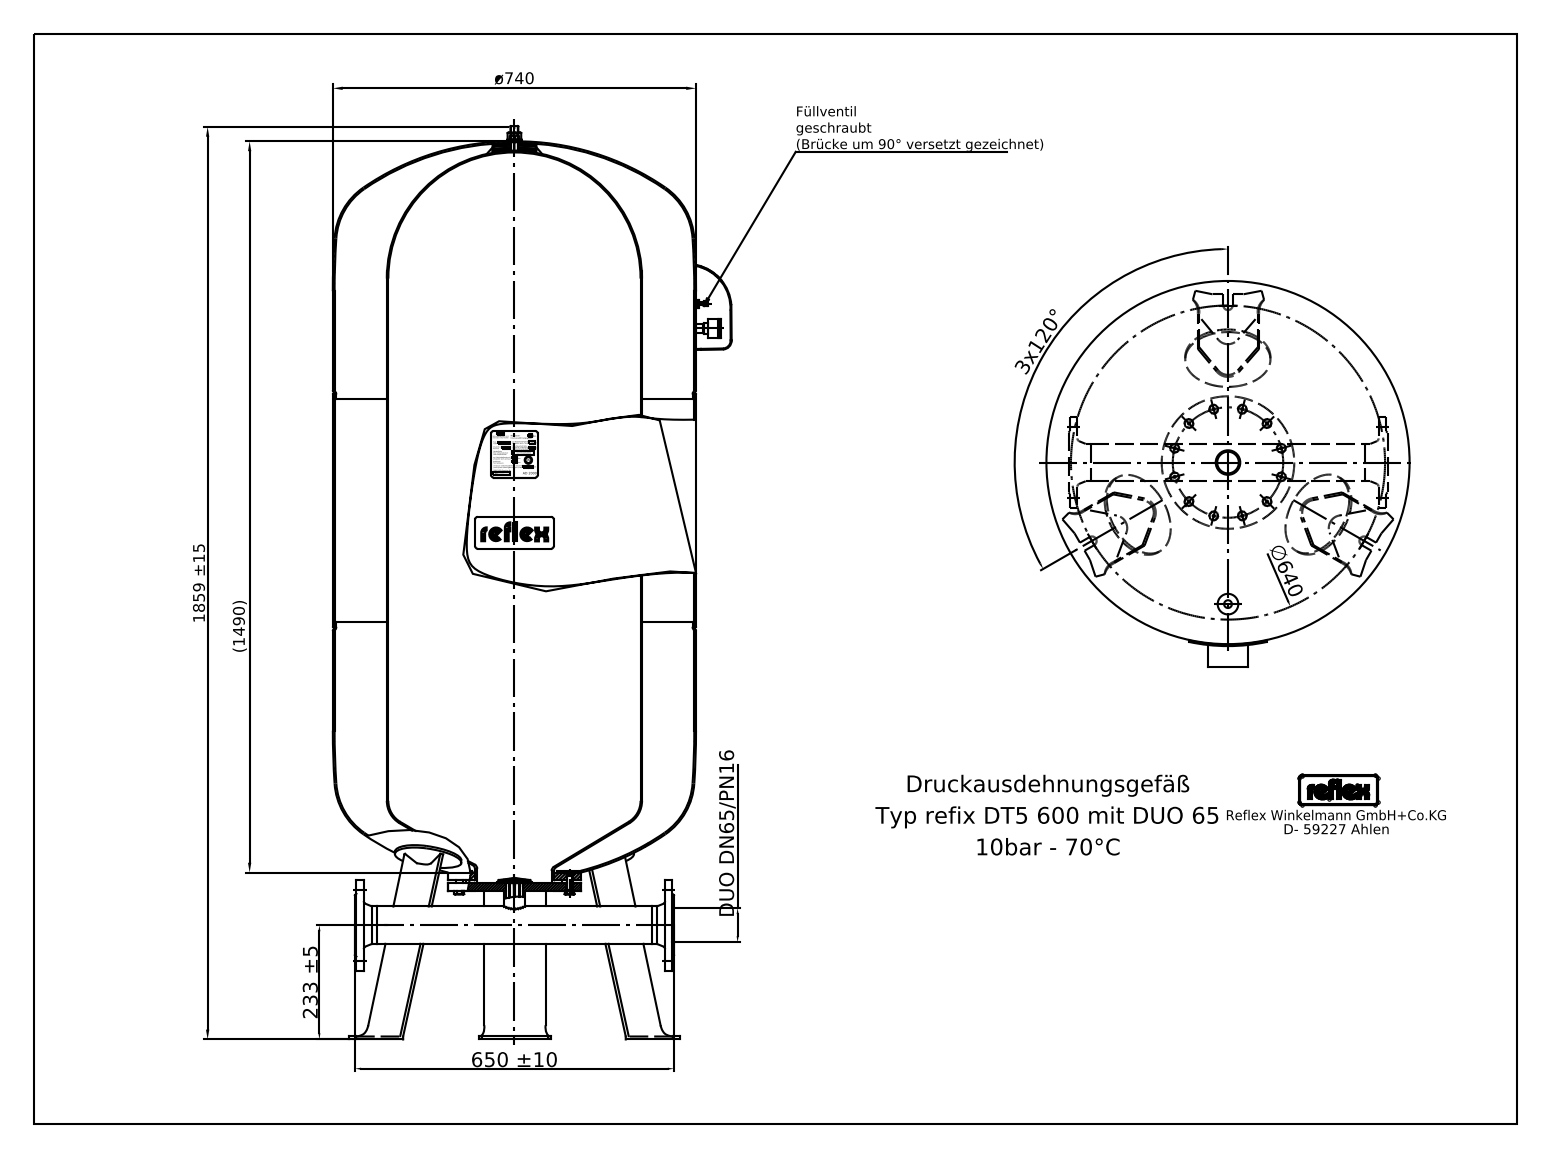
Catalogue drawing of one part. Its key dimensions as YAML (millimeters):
step_written_by: "Mechanical Desktop 2008 (CONFIG_CONTROL_DESIGN)"
units: millimeters
bodies: {solids: 26, faces: 522, planar: 233, cylindrical: 155, other: 134}
overall_size: [1859, 810.1, 740]
volume: 598000000
surface_area: 6780000
round_holes:
  - {diameter: 19, count: 4}
  - {diameter: 2.48, count: 1}
  - {diameter: 3.8, count: 1}
  - {diameter: 4.3, count: 1}
  - {diameter: 4.4, count: 1}
  - {diameter: 5.45, count: 1}
  - {diameter: 7, count: 1}
  - {diameter: 8, count: 1}
  - {diameter: 11.4, count: 1}
  - {diameter: 76.1, count: 1}
  - {diameter: 157, count: 1}
  - {diameter: 250, count: 1}
round_bosses_or_shafts:
  - {diameter: 10, count: 9}
  - {diameter: 740, count: 1}
  - {diameter: 260, count: 1}
  - {diameter: 230, count: 1}
  - {diameter: 185, count: 1}
  - {diameter: 62, count: 1}
  - {diameter: 42.4, count: 1}
  - {diameter: 34, count: 1}
partial_cylinders:
  - {radius: 25, count: 18}
  - {radius: 5.62, count: 4}
  - {radius: 2.25, count: 3}
  - {radius: 9, count: 3}
  - {radius: 3.84, count: 2}
  - {radius: 6.75, count: 2}
  - {radius: 8, count: 2}
  - {radius: 9.27, count: 2}
face_to_face_distances: [1127, 6, 195, 1322, 5.97, 5.89, 201, 1328, 313, 5]
hole_center_spacings: [72.51, 102.54, 145.01, 50]
